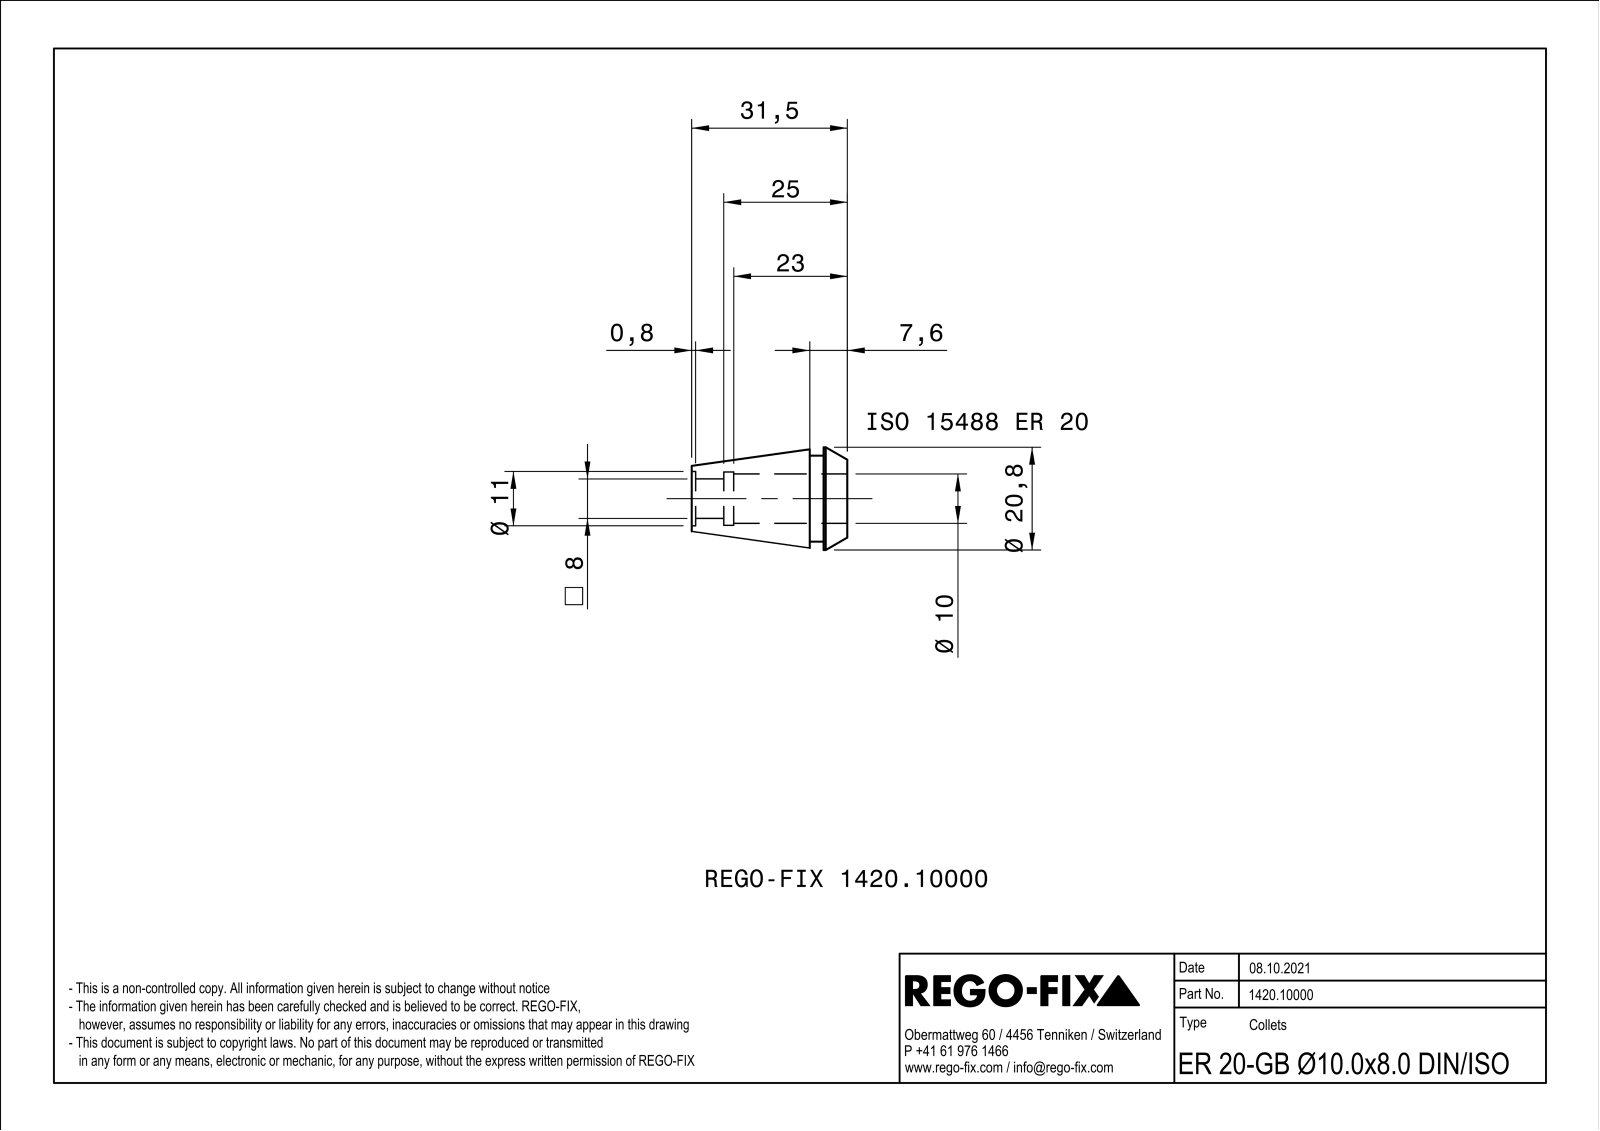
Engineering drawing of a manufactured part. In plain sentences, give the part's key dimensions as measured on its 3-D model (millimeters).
The part is named "NOCUT". Its 3-D file was written by "SIEMENS PLM Software Solid Edge ST10 (AUTOMOTIVE_DESIGN)". It is 1 solid with 144 faces: 60 planar, 32 cylindrical and 52 other. Overall it measures 31.5 by 20.79 by 20.79 millimeters. Its volume is 4 103 cubic millimeters and its surface area 4 230 square millimeters. Round holes: 1 of diameter 10, 1 of diameter 10.8, 1 of diameter 11. Round bosses or shafts: 1 of diameter 17.4. Partial cylindrical surfaces (rounded edges, fillets, slot ends): 1 of radius 4.55, 1 of radius 5.25. The main face-to-face distances are 0.8, 4.8, 7.6, 2.8, 3.85, 4.65, 8.5, 31.5, 26.7, 23.9.
